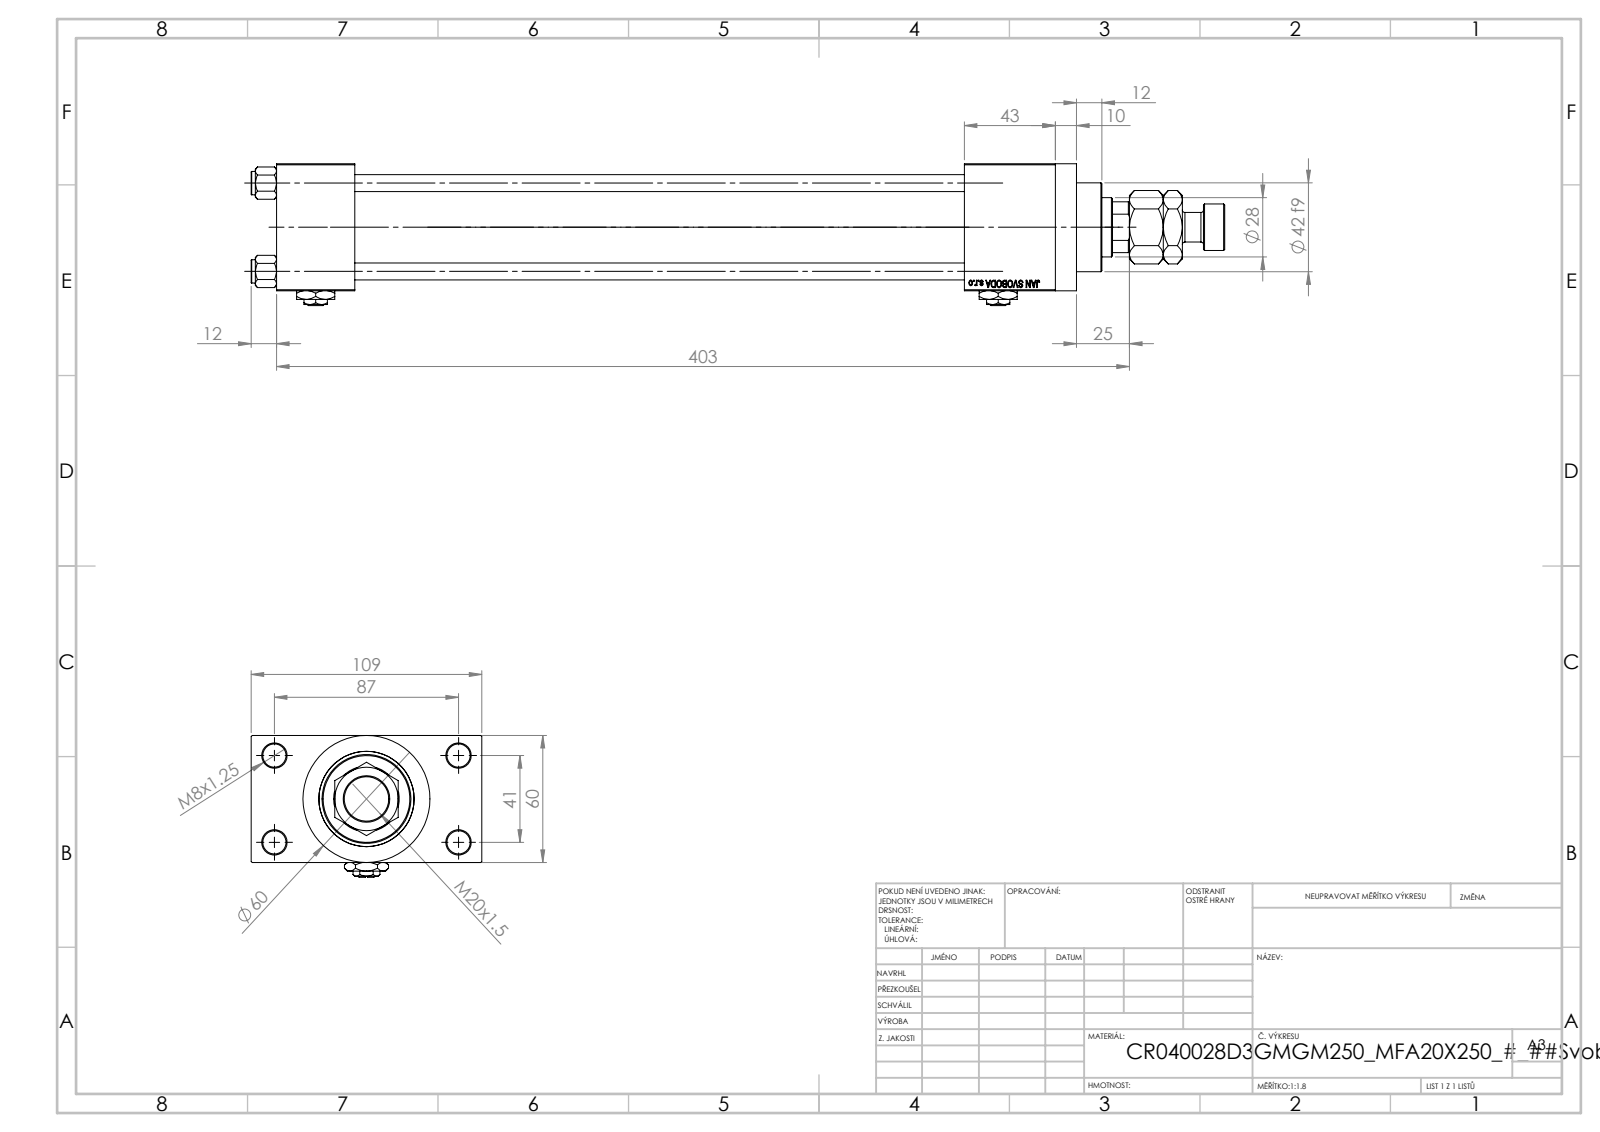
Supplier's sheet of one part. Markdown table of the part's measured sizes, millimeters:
| quantity | value |
| --- | --- |
| part name | V215CR_D_TYCINKA; V215_VC_A; V215CR_VCP_D; MFA (+3 more) |
| STEP written by | SolidWorks 2019 (CONFIG_CONTROL_DESIGN) |
| units | millimeters |
| bodies | 14 solids, 1257 faces (562 planar, 103 cylindrical, 592 other) |
| overall size | 460 × 109 × 67 |
| volume | 832 727 mm³ |
| surface area | 242 748 mm² |
| round holes (diameter × count) | 8 × 4, 11 × 4, 16.66 × 4, 24 × 4, 7 × 3, 18.5 × 1, 28 × 1, 31 × 1, 40 × 1, 45 × 1 |
| round bosses / shafts (diameter × count) | 11 × 4, 60 × 1, 46 × 1, 42 × 1, 22 × 1, 14 × 1 |
| partial cylindrical surfaces (radius × count) | 13.5 × 1 |
| main face-to-face distances | 60, 24.5, 288, 84.5, 37, 325, 43, 368, 331, 109 |
| hole center spacings | 22.65, 29.49, 41.7, 47.15, 48.09, 64.35, 76.49, 41 |
